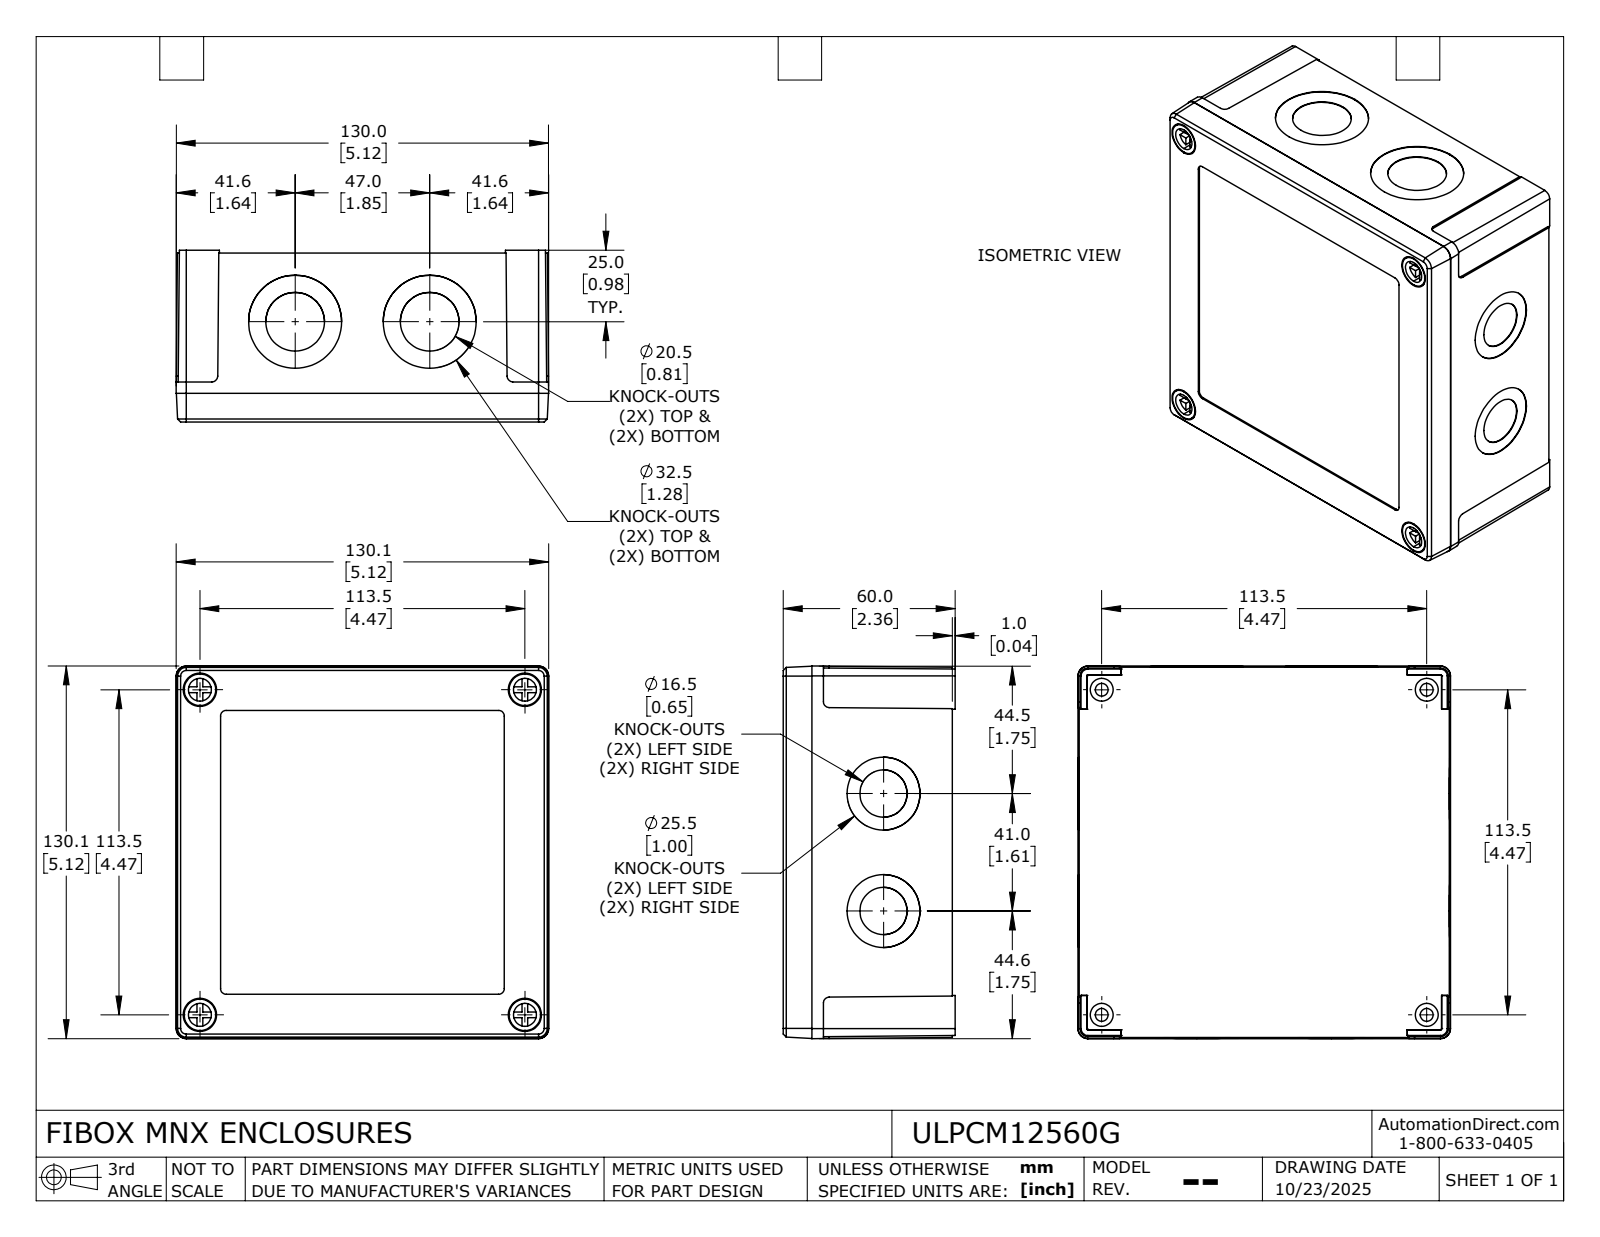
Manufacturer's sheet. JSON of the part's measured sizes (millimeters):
{"part_name": "ULPCM12560G_Default", "step_written_by": "SolidWorks 2024 (CONFIG_CONTROL_DESIGN)", "units": "millimeters", "bodies": {"solids": 6, "faces": 522, "planar": 298, "cylindrical": 184, "other": 40}, "overall_size": [130.1, 130.1, 60], "volume_mm3": 216000, "surface_area_mm2": 136200, "round_holes": [[3.2, 8], [4, 8], [4.5, 4], [8, 4], [11.6, 4], [16.5, 4], [20.5, 4], [25.5, 4], [32.5, 4]], "round_bosses_or_shafts": [[8, 8], [2.5, 8], [11, 4], [7.2, 4]], "partial_cylinders_radius": [[2, 8], [1.4, 6], [0.5, 4], [5, 4], [0.6, 2]], "face_to_face_distances": [4.2, 56.7, 3, 53.7, 58.5, 55.5, 1.8, 56, 59, 2.3], "hole_center_spacings": [57.9, 116.5, 22.6, 37.5, 45.6, 63.7, 90, 94]}
